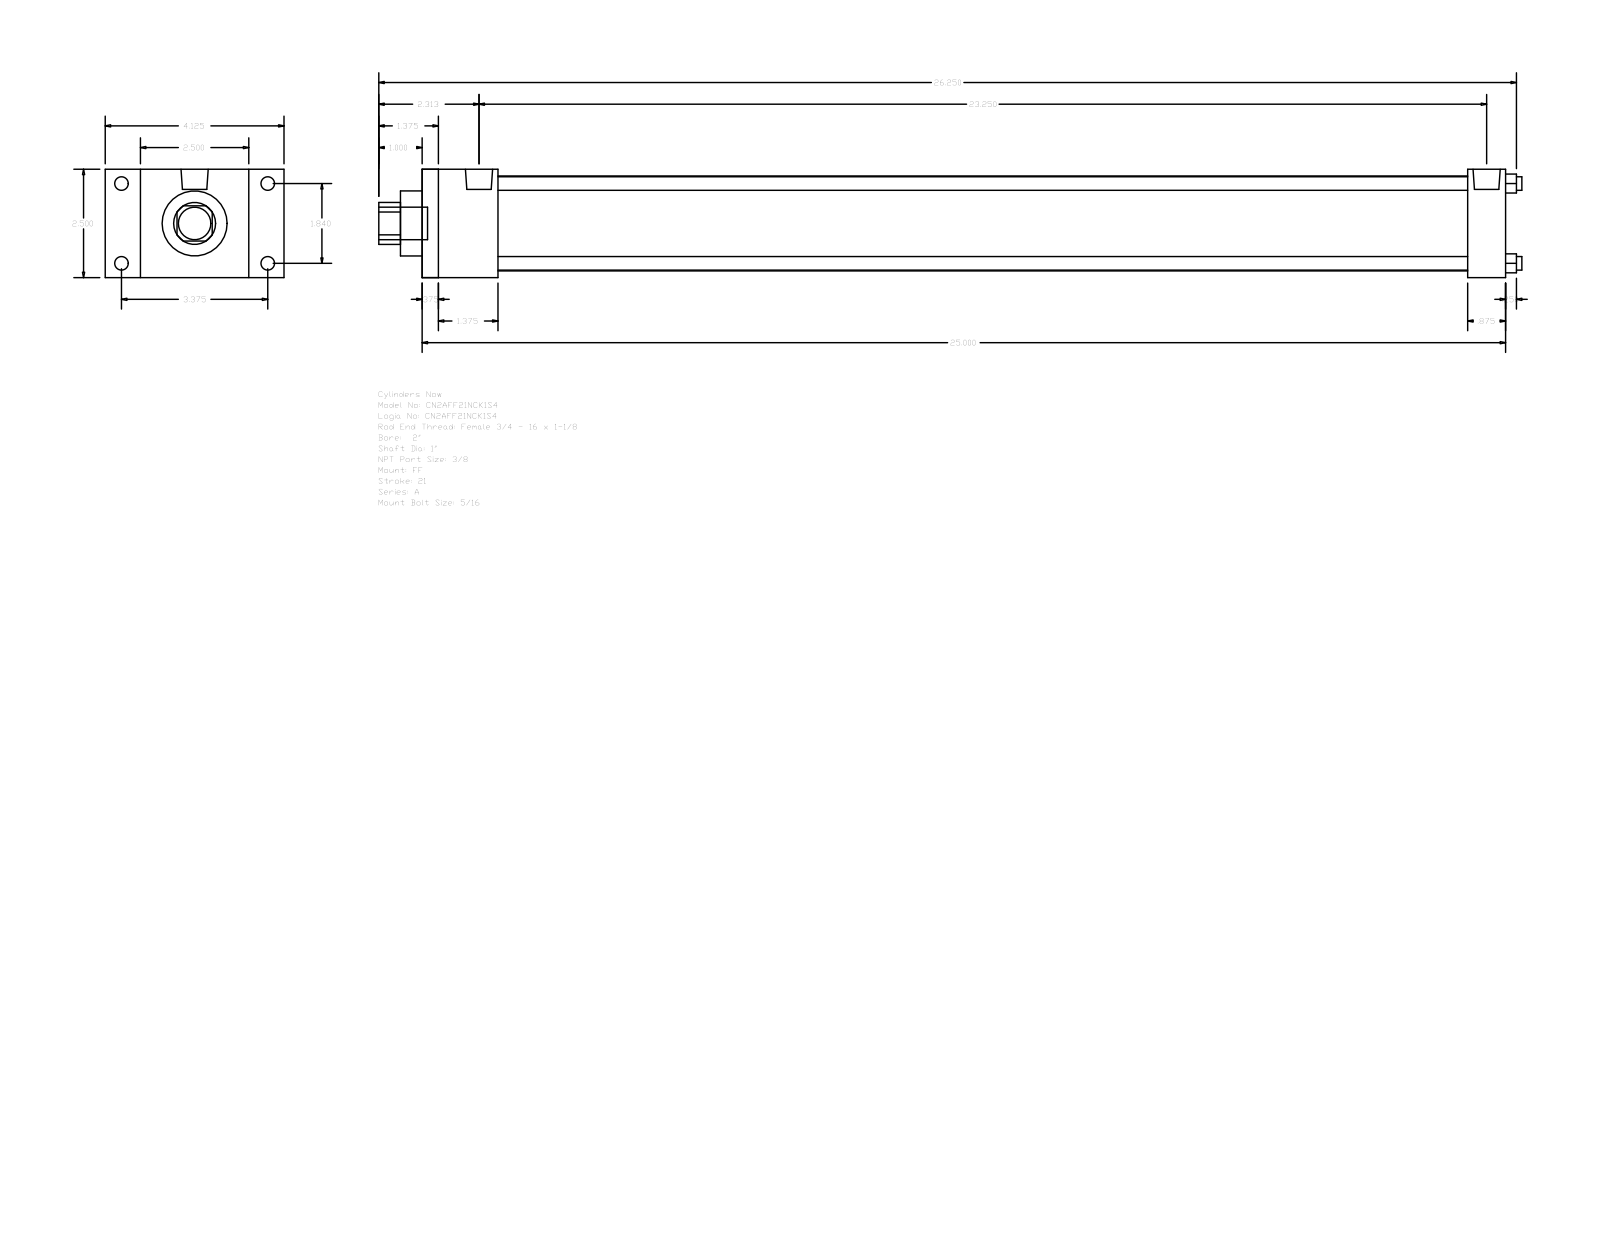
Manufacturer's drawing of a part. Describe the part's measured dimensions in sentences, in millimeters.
The part is named "A_FF__0200_1". Its 3-D file was written by "GSSL Pune (CONFIG_CONTROL_DESIGN)". It is 0 solids with 92 faces: 64 planar, 28 cylindrical and 0 other. Overall it measures 669.92 by 104.78 by 63.5 millimeters. Round holes: 4 of diameter 7.94, 1 of diameter 25.4, 1 of diameter 38.1, 1 of diameter 55.63. Round bosses or shafts: 4 of diameter 7.94, 4 of diameter 5.56, 2 of diameter 15.93, 1 of diameter 19.05. Partial cylindrical surfaces (rounded edges, fillets, slot ends): 1 of radius 12.29. The main face-to-face distances are 63.5, 635, 9.52, 625.48, 20.64, 44.45, 612.77, 34.93, 603.25, 568.32. The hole center spacings are 33.05, 46.74, 66.1.
